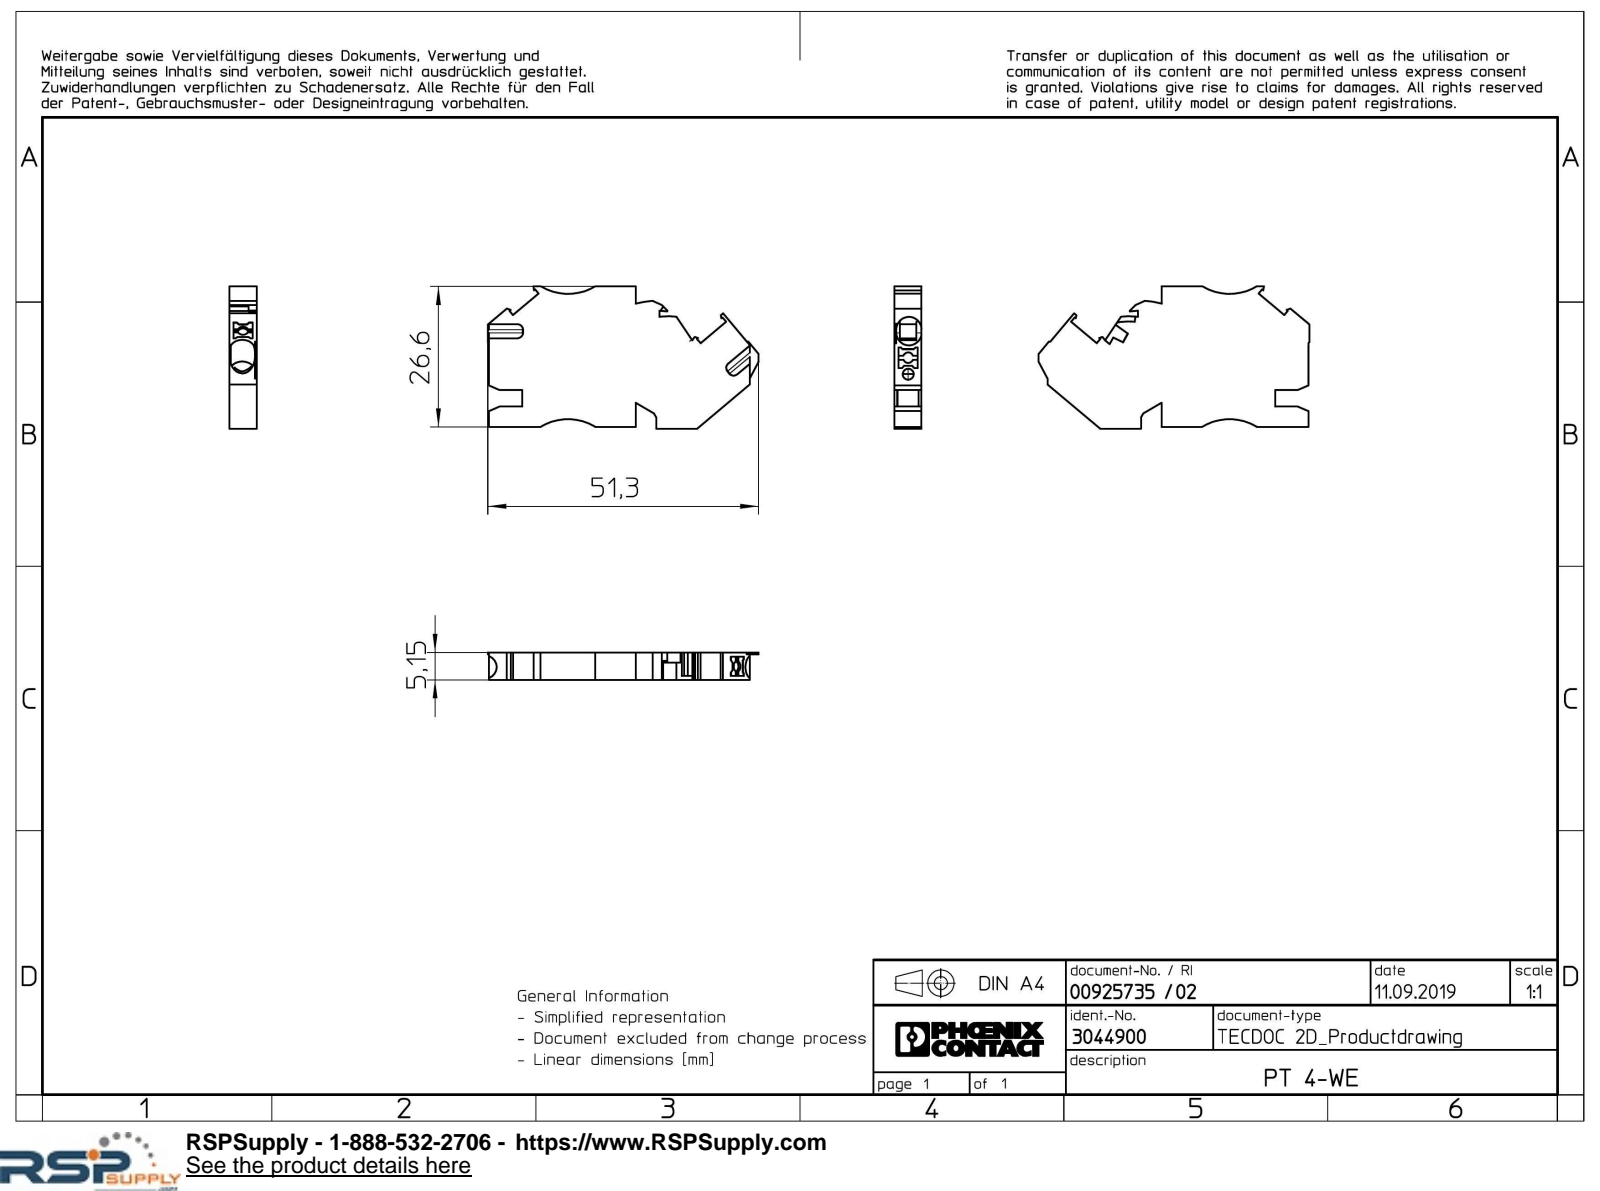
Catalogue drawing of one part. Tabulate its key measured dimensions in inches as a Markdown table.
| quantity | value |
| --- | --- |
| part name | PT_4_WE-select |
| STEP written by | Creo Elements/Direct Modeling 20.1A 29-Sep-2018 (C) Parametric Technology GmbH (AUTOMOTIVE_DESIGN) |
| units | inches |
| bodies | 1 solid, 161 faces (139 planar, 20 cylindrical, 2 other) |
| overall size | 2.02 × 1.059 × 0.203 |
| volume | 0.28 in³ |
| surface area | 5.721 in² |
| round holes (diameter × count) | 0.083 × 1 |
| partial cylindrical surfaces (radius × count) | 0.094 × 4, 0.041 × 3, 0.039 × 2, 0.394 × 2, 0.041 × 1, 0.07 × 1, 0.488 × 1, 0.527 × 1 |
| main face-to-face distances | 0.203, 0.152, 0.124, 0.276, 0.043, 0.159, 0.165, 0.122, 0.037, 1.047 |
